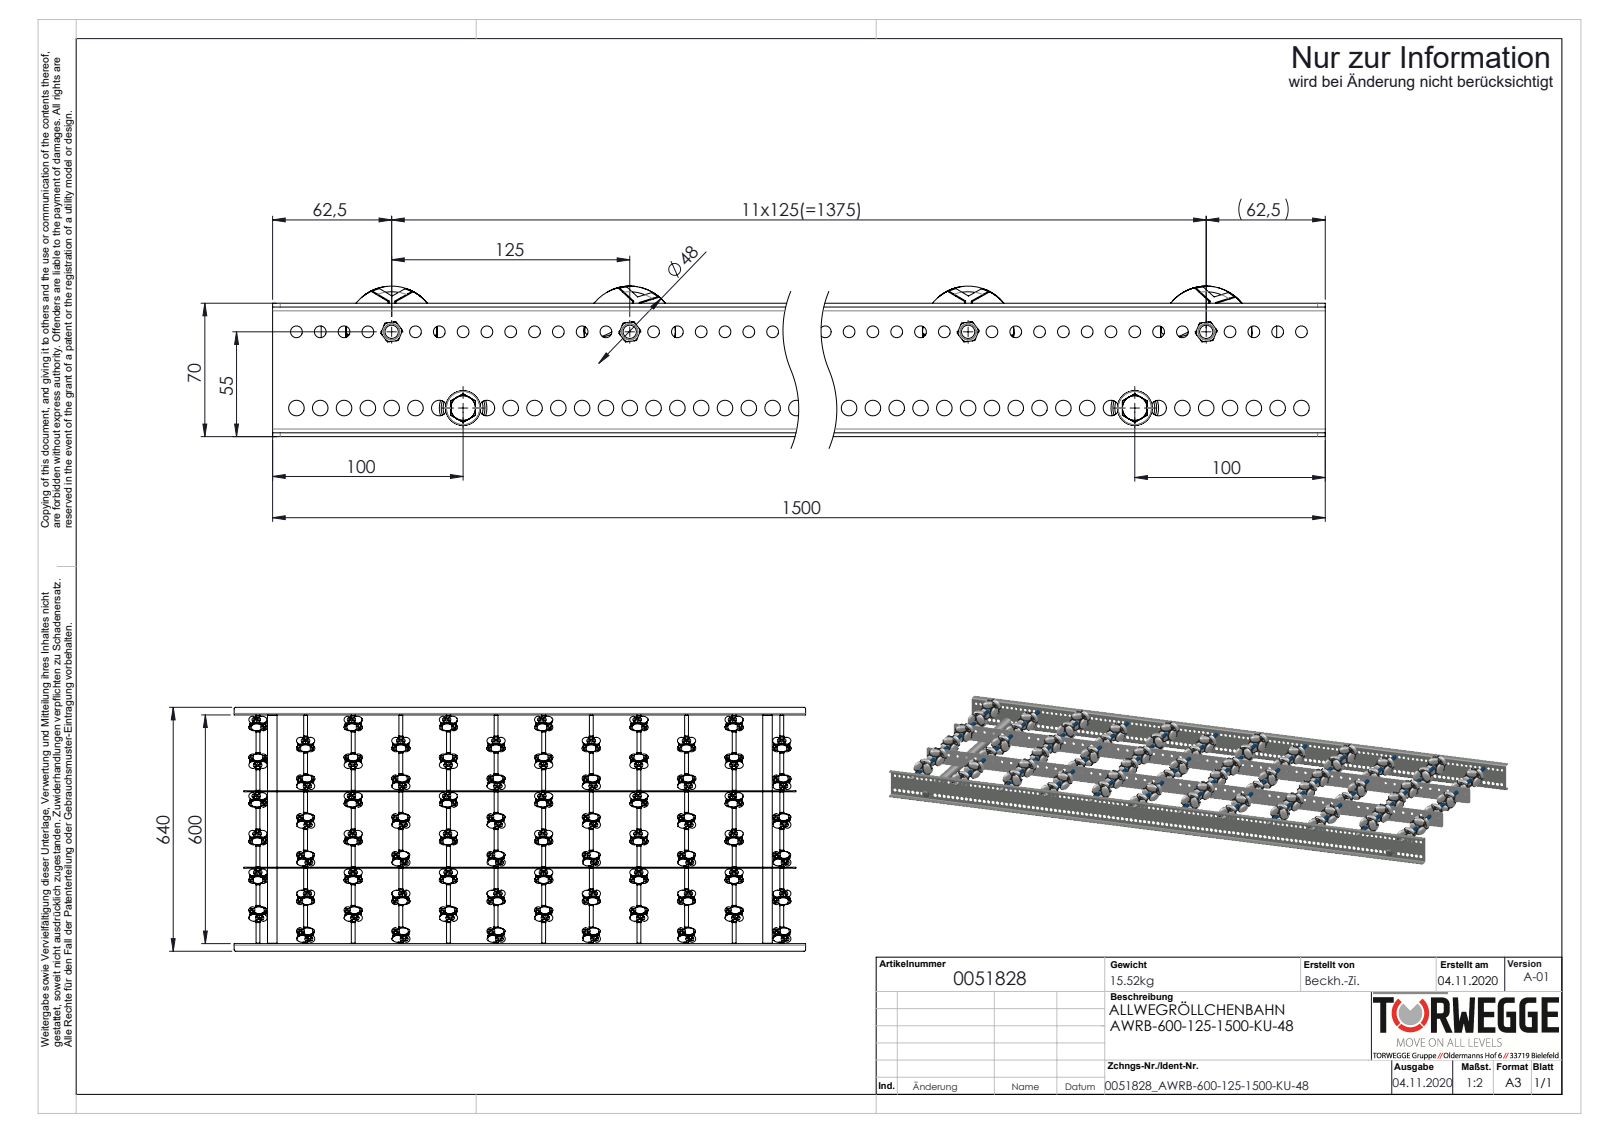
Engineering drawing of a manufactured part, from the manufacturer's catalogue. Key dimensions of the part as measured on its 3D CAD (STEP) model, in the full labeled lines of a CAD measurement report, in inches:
Part name (STEP PRODUCT): 0019719_Gewindestange-M6_L=620; AWR48_Röllchen; 0015028_AWR48; AWR48_Stift (+8 more)
STEP written by: SolidWorks 2020 (AUTOMOTIVE_DESIGN)
Units: inches
Bodies: 1202 solids, 21860 faces (7404 planar, 8856 cylindrical, 5600 other)
Overall size (bounding box): 59.055 × 25.197 × 3.11
Volume: 276.4 in³ · Surface area: 5 008 in²
Round holes (diameter × count): ⌀0.146 ×432, ⌀0.165 ×432, ⌀0.244 ×119, ⌀0.323 ×119, ⌀0.256 ×58, ⌀0.194 ×12, ⌀0.331 ×12, ⌀0.268 ×2, ⌀0.827 ×2
Round bosses / shafts (diameter × count): ⌀0.157 ×432, ⌀0.146 ×368, ⌀0.315 ×14, ⌀1.854 ×12, ⌀1.654 ×12, ⌀0.433 ×12, ⌀0.394 ×12, ⌀0.276 ×12
Partial cylindrical surfaces — rounded edges, fillets, slot ends (radius × count): R0.157 ×8, R0.079 ×4, R0.197 ×4
Main face-to-face distances: 0.079, 23.701, 7.894, 0.098, 2.677, 23.622, 23.78, 7.917, 15.811, 7.839
Hole centre spacings: 1.419, 1.42, 1.42, 1.419, 0.305, 0.394, 0.61, 2.176
